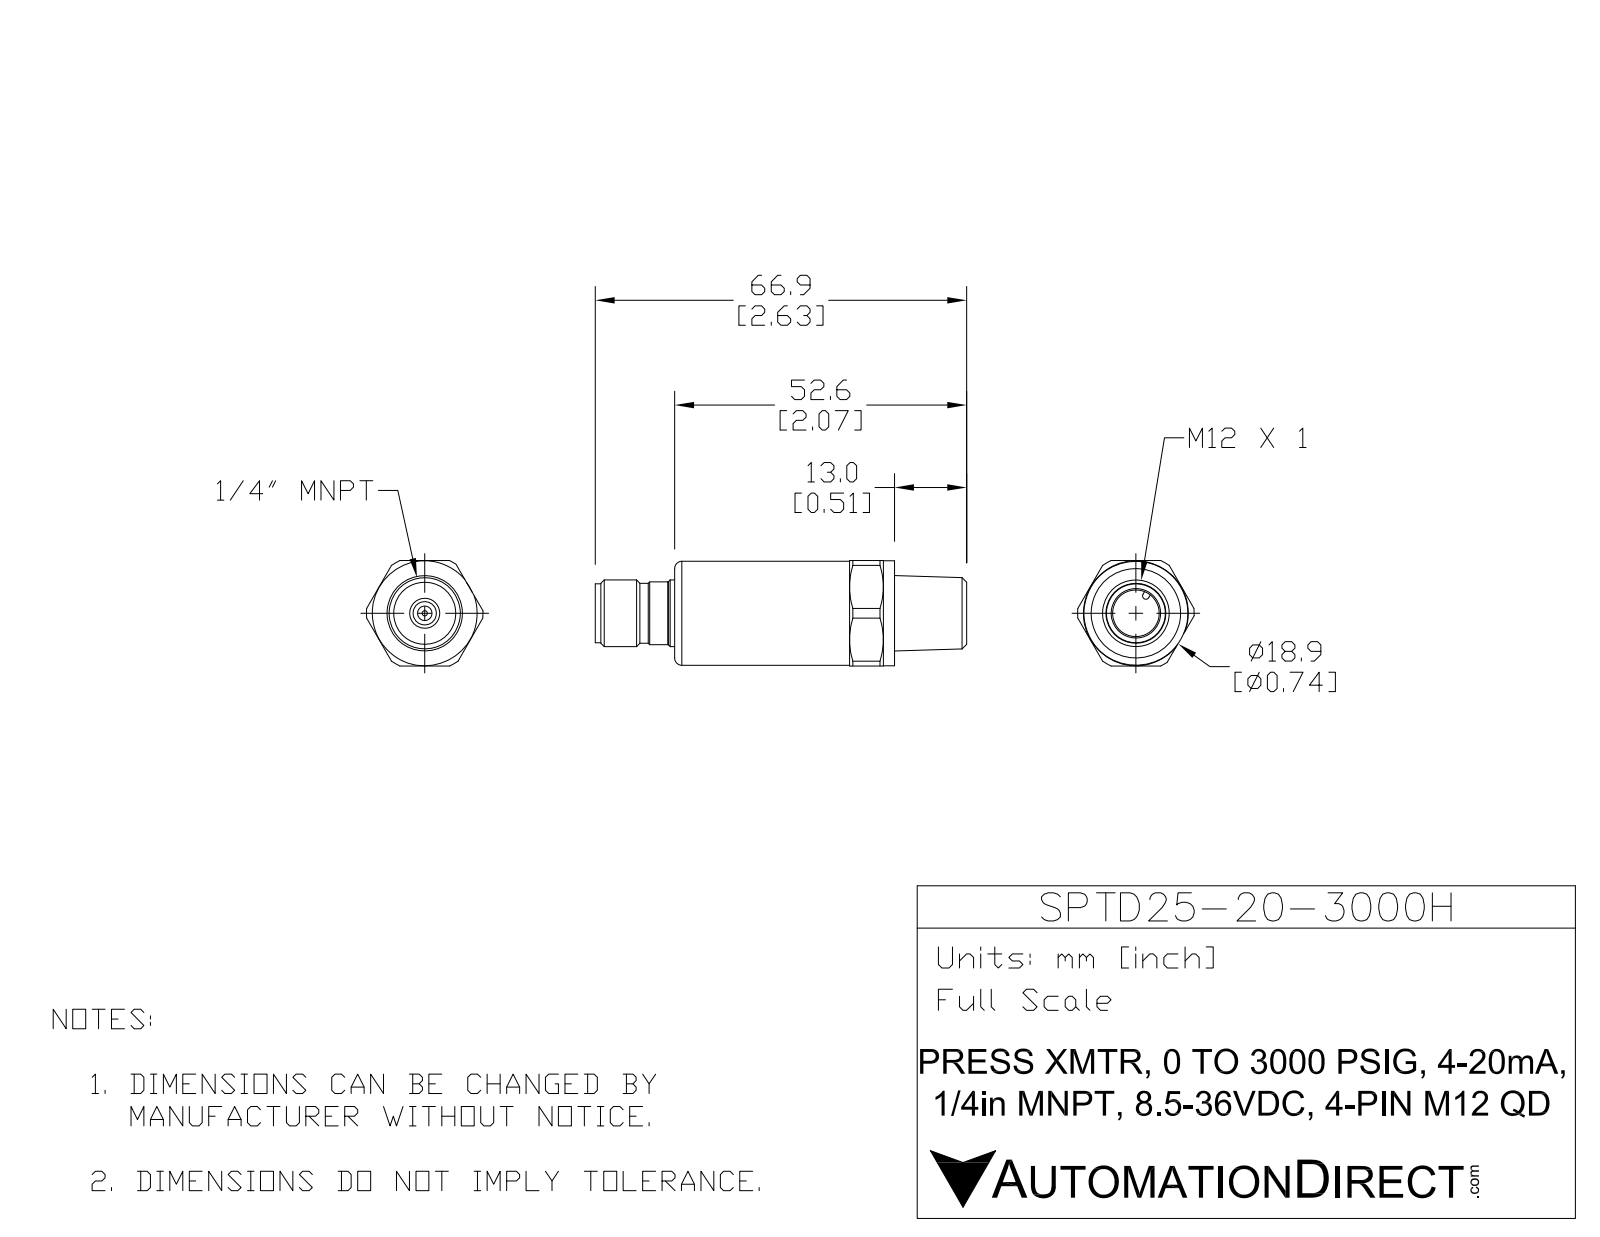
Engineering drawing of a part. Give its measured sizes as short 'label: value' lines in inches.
name: SPDT25-20-3000H
written by: SolidWorks 2015 (AUTOMOTIVE_DESIGN)
unit: in
bodies: 7 solids, 177 faces (44 planar, 53 cylindrical, 80 other)
size: 2.634 × 0.849 × 0.744
volume: 0.821 in³; area: 8.272 in²
holes: 1× ⌀0.165, 1× ⌀0.331, 1× ⌀0.654
bosses: 4× ⌀0.055, 4× ⌀0.039, 1× ⌀0.744, 1× ⌀0.472, 1× ⌀0.445, 1× ⌀0.425, 1× ⌀0.417, 1× ⌀0.413
rounds: 1× R0.024
face distances: 0.744, 2.069, 0.515, 1.554, 2.287, 1.772, 0.219, 0.563, 0.047, 1.506
